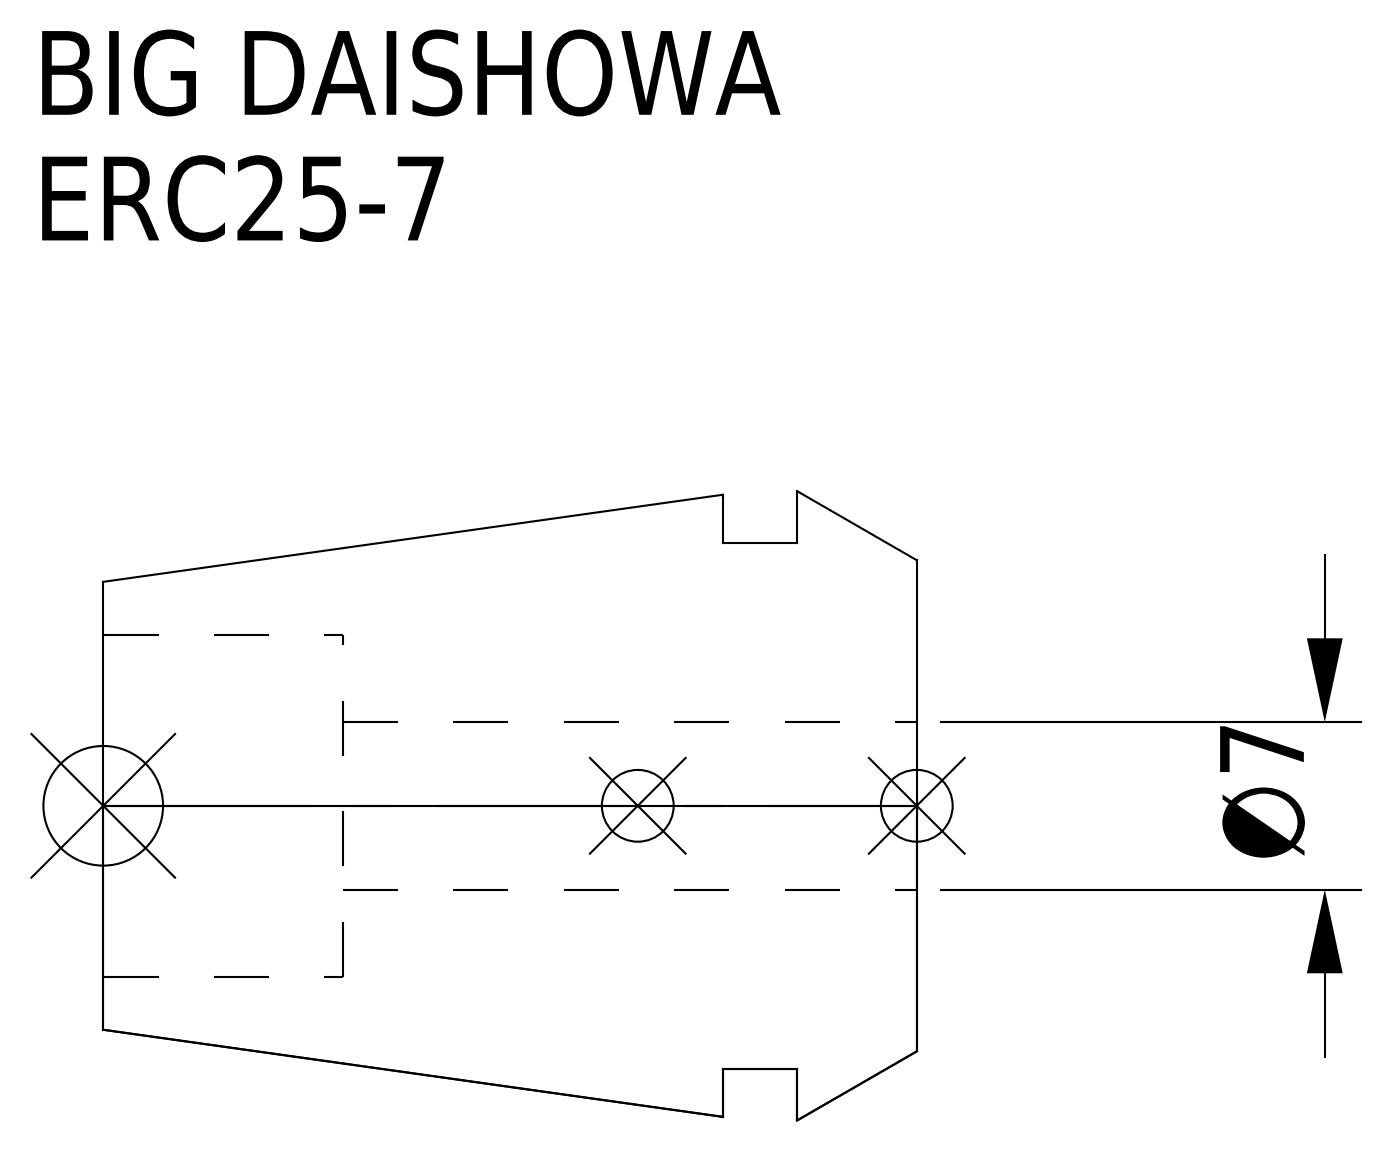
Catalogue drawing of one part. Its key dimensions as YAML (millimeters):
part_name: "ERC25-7"
step_written_by: "CREO PARAMETRIC BY PTC INC, 2016380 (AUTOMOTIVE_DESIGN)"
units: millimeters
bodies: {solids: 1, faces: 15, planar: 5, cylindrical: 6, other: 4}
overall_size: [34, 26.3, 26.3]
volume: 11073
surface_area: 4296
round_holes:
  - {diameter: 7, count: 1}
  - {diameter: 14.3, count: 1}
round_bosses_or_shafts:
  - {diameter: 22, count: 1}
face_to_face_distances: [5, 8.1, 3.1, 24, 19, 15.9, 34, 29, 25.9, 10]
